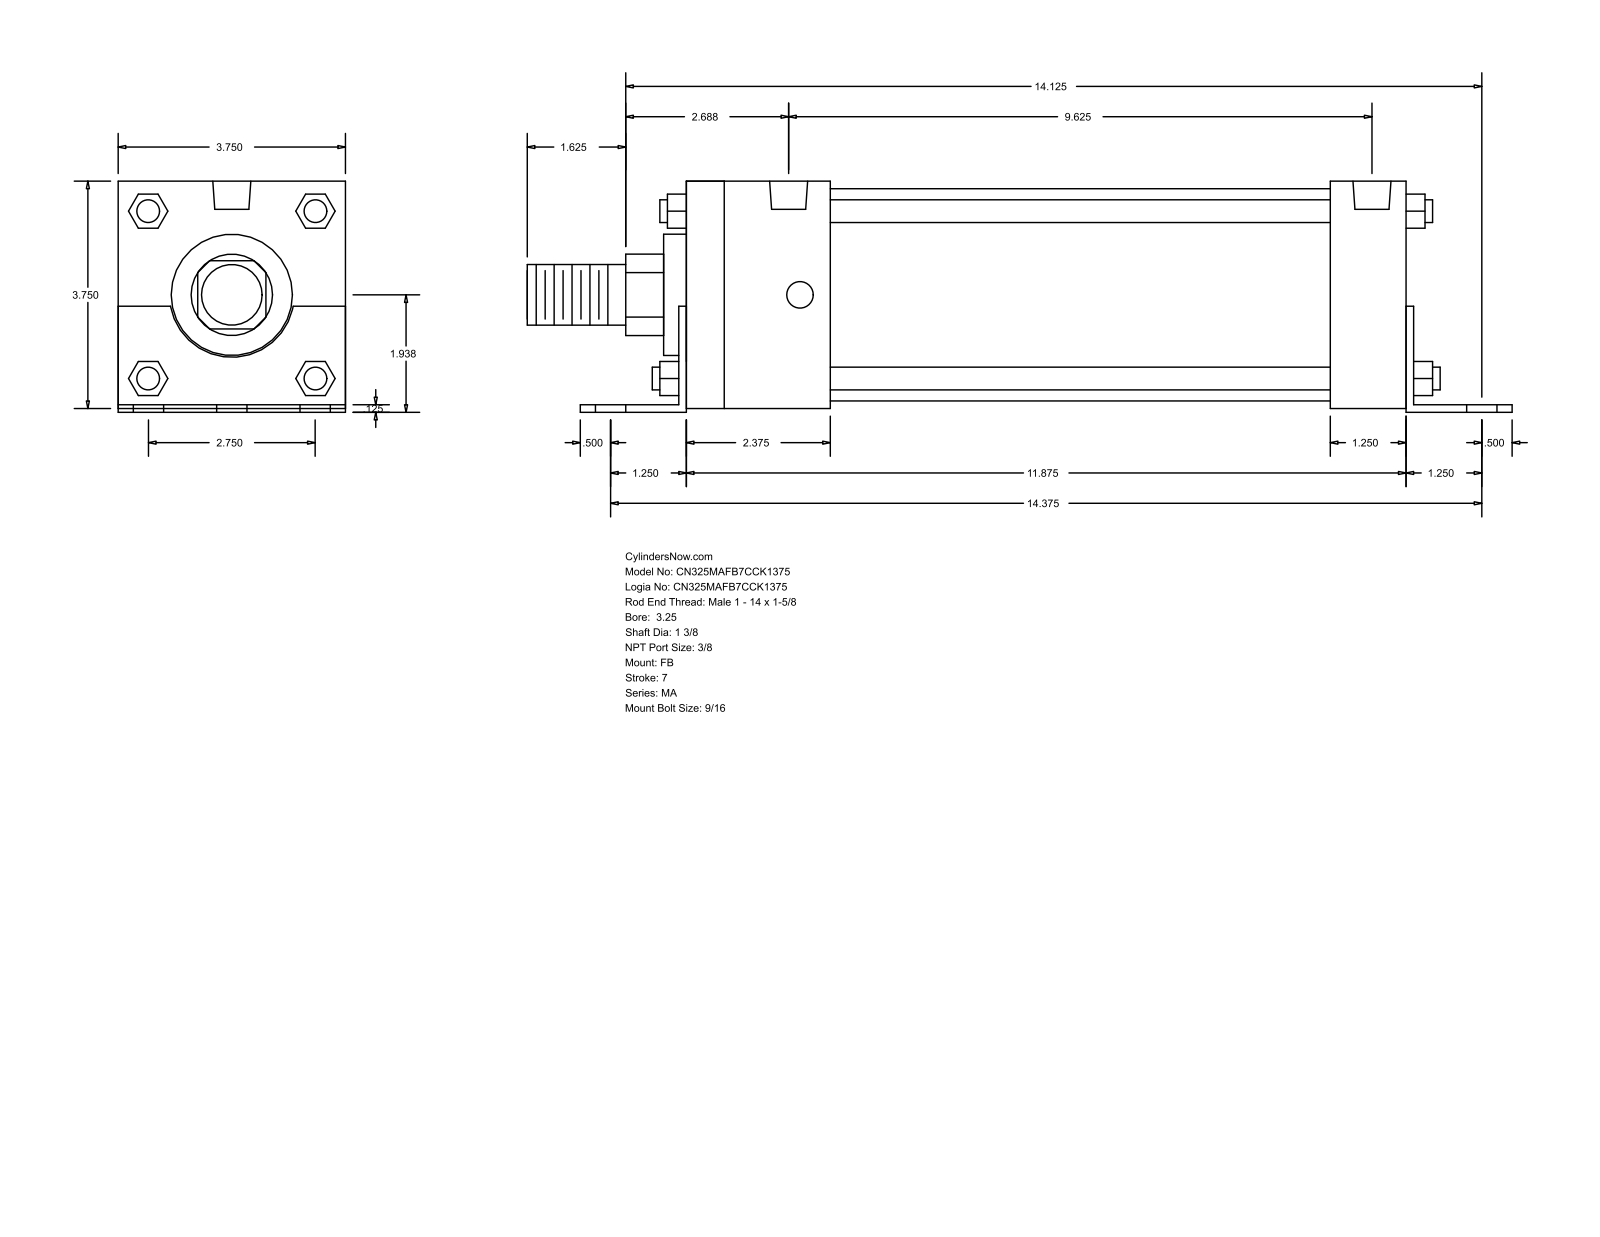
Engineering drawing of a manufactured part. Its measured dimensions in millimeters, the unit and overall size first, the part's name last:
Units: millimetres
Overall size (bounding box): 412.75 × 96.84 × 95.25
Round holes (diameter × count): ⌀14.29 ×6, ⌀11.11 ×4, ⌀15.93 ×2
Round bosses / shafts (diameter × count): ⌀9.53 ×4, ⌀88.9 ×1, ⌀50.8 ×1, ⌀34.92 ×1, ⌀25.4 ×1
Partial cylindrical surfaces — rounded edges, fillets, slot ends (radius × count): R17.06 ×1, R26.16 ×1
Main face-to-face distances: 95.24, 3.17, 1.59, 96.83, 1.58, 93.66, 3.18, 301.62, 304.8, 31.75
Hole centre spacings: 34.92, 366.79, 365.12, 57.78, 61.64, 69.84, 82.38, 86.72
Bodies: 0 solids, 140 faces (105 planar, 35 cylindrical, 0 other)
Part name (STEP PRODUCT): MA_FB__0325_1.375
STEP written by: GSSL Pune (CONFIG_CONTROL_DESIGN)
